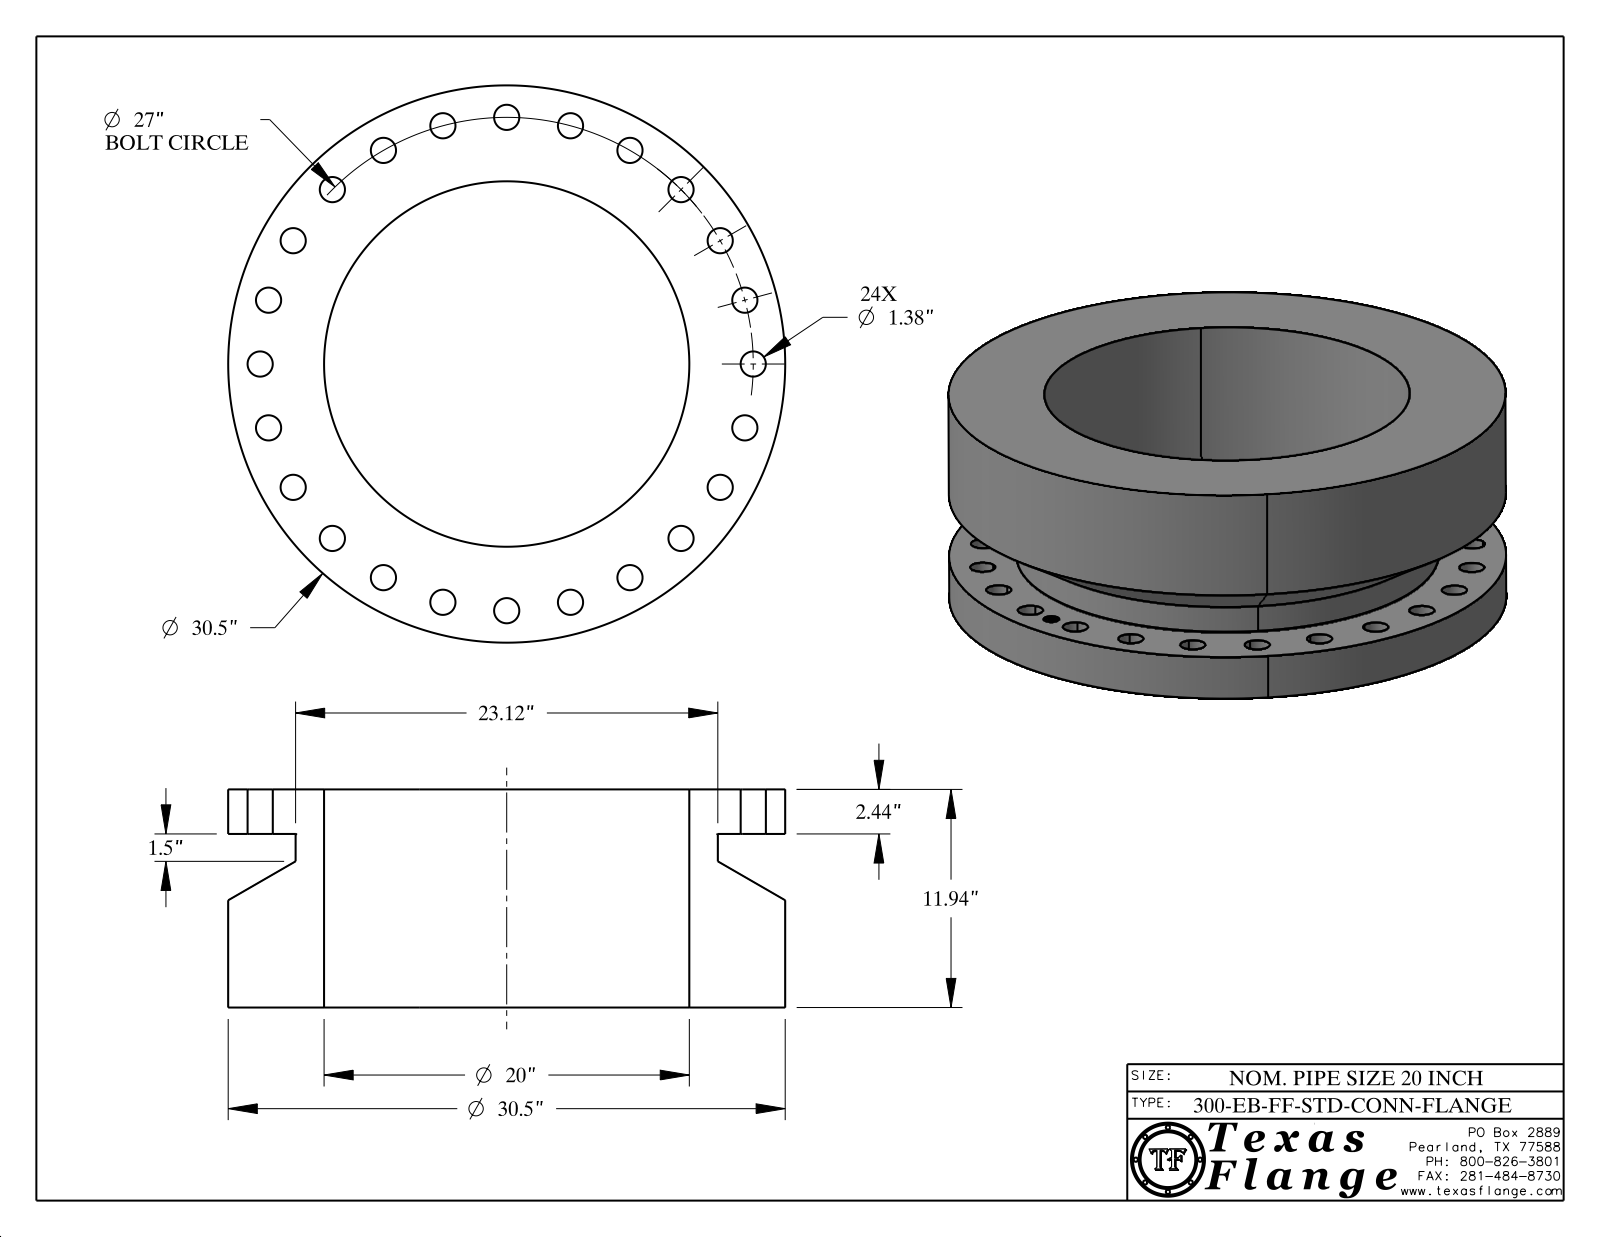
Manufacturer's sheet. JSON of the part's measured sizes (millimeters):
{"part_name": "20-300-EB-FF-STD-CONN-FLANGE", "step_written_by": "CATIA V5 STEP AP214 (AUTOMOTIVE_DESIGN)", "units": "millimeters", "bodies": {"solids": 1, "faces": 450, "planar": 368, "cylindrical": 76, "other": 6}, "overall_size": [774.7, 774.7, 303.2], "volume_mm3": 66710000, "surface_area_mm2": 2156000, "round_holes": [[35.1, 24], [21.6, 1], [508, 1]], "round_bosses_or_shafts": [[1.3, 8], [774.7, 1], [587.2, 1], [17, 1]], "face_to_face_distances": [303.2, 61.9, 241.3, 61.8, 241.4, 6.5, 6.3, 0.4, 1.2, 4.2], "hole_center_spacings": [342.9, 89.5, 177.5, 262.5, 417.5, 633.6, 679.9, 544.1]}
